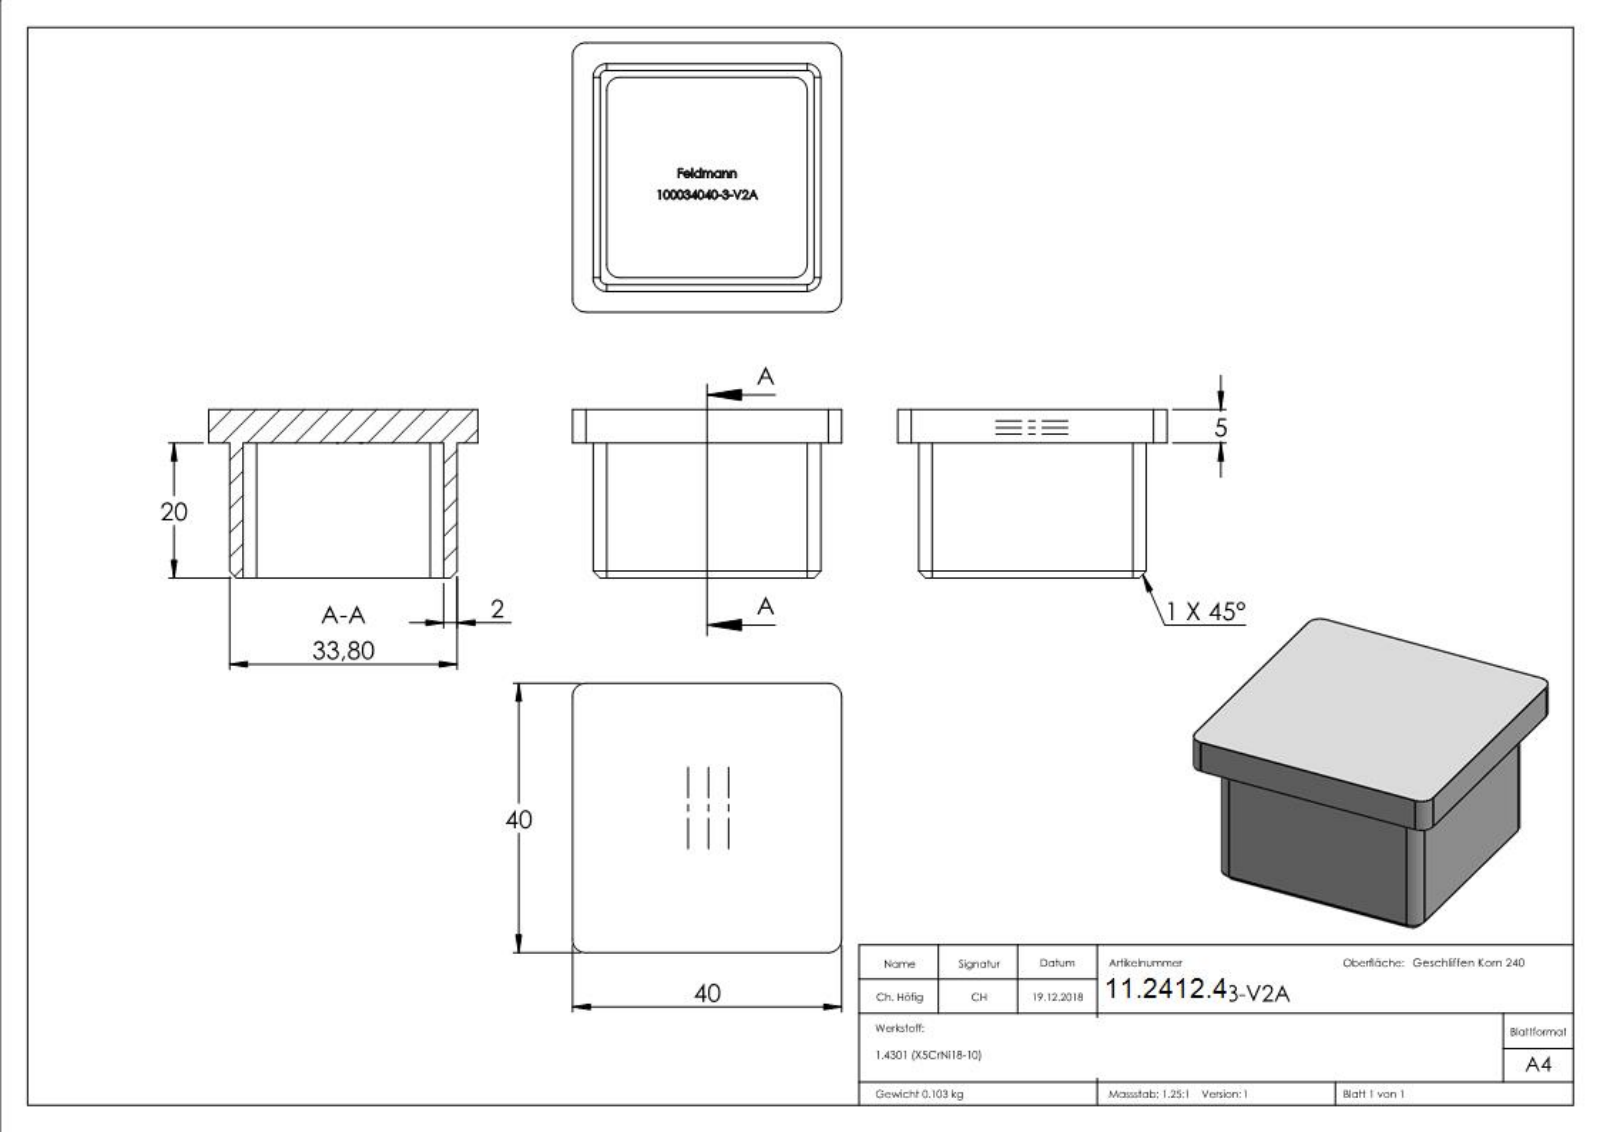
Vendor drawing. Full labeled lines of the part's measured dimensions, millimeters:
Part name (STEP PRODUCT): 100034040-3-V2A
STEP written by: SolidWorks 2015 (CONFIG_CONTROL_DESIGN)
Units: millimetres
Bodies: 1 solid, 321 faces (178 planar, 12 cylindrical, 131 other)
Overall size (bounding box): 40 × 40 × 25
Volume: 13 005 mm³ · Surface area: 8 861 mm²
Partial cylindrical surfaces — rounded edges, fillets, slot ends (radius × count): R2 ×12
Main face-to-face distances: 2, 31.8, 5, 33.8, 29.8, 3.1, 5.1, 34.9, 36.9, 40
